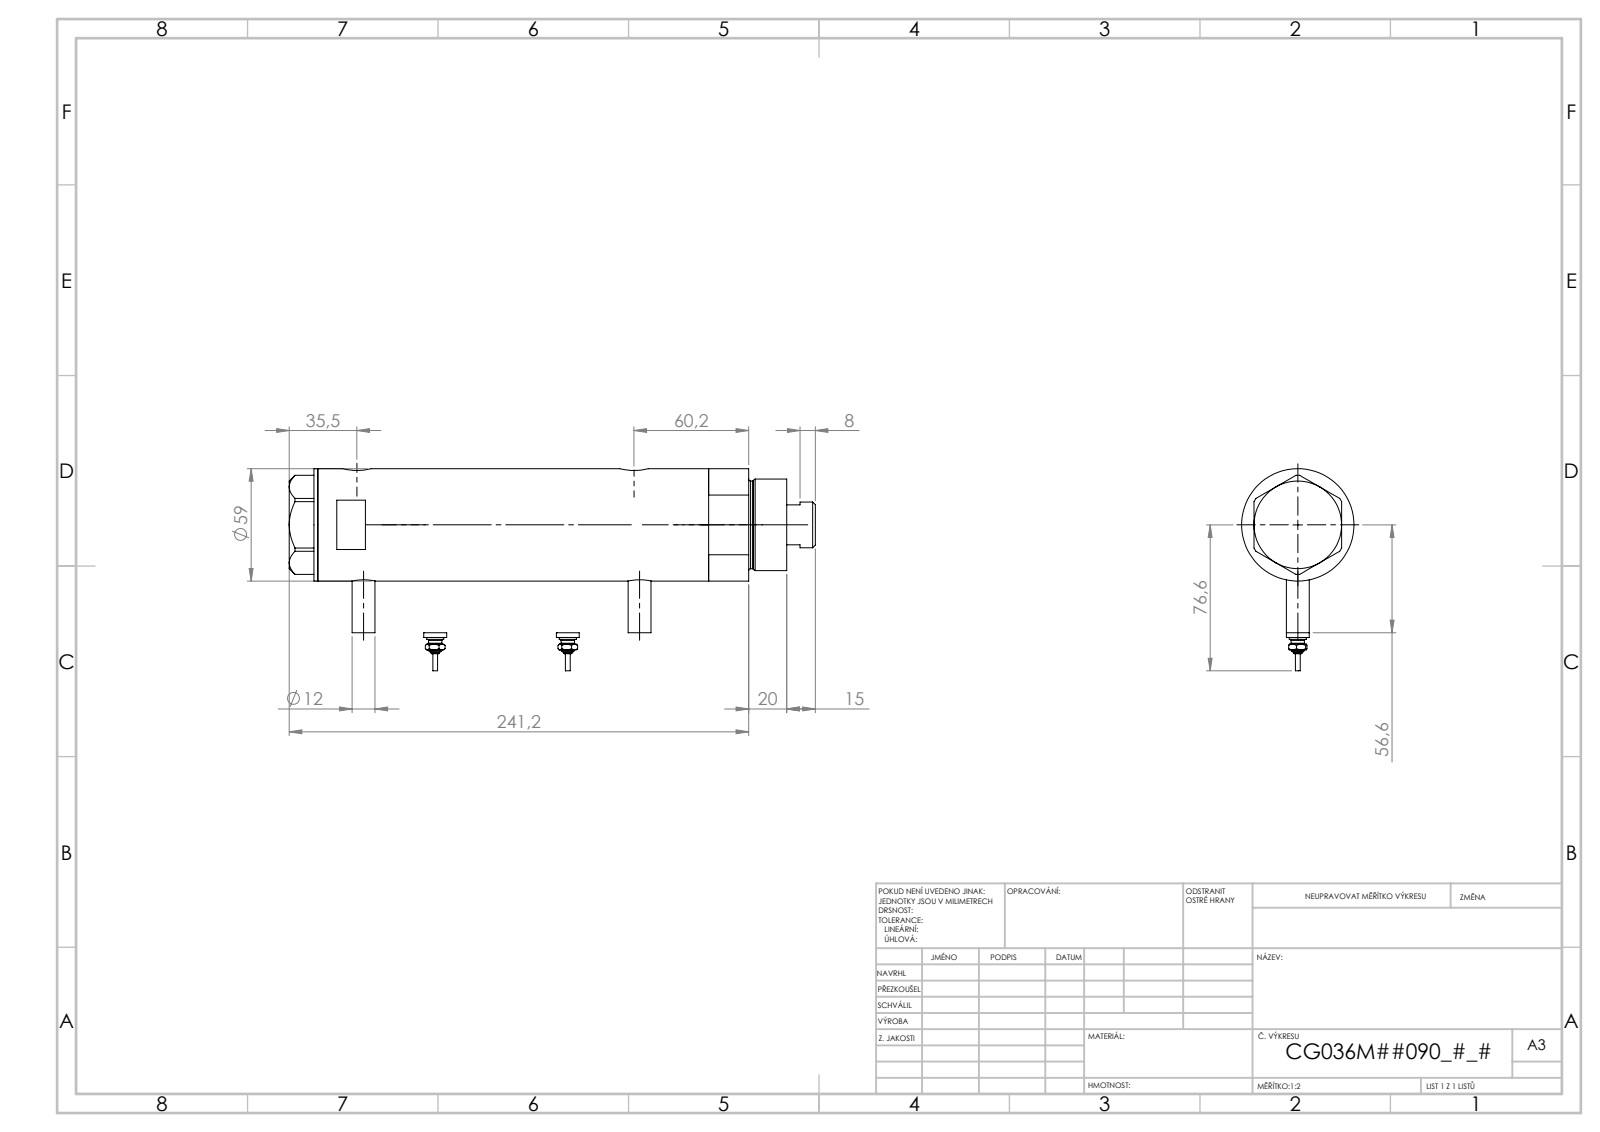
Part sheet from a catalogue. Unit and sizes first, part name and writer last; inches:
Units: inches
Overall size (bounding box): 9.977 × 3.594 × 2.323
Round holes (diameter × count): ⌀0.197 ×2, ⌀0.383 ×2, ⌀0.492 ×2, ⌀0.591 ×2, ⌀0.335 ×1, ⌀0.984 ×1, ⌀1.043 ×1, ⌀1.417 ×1, ⌀1.575 ×1, ⌀2.047 ×1
Round bosses / shafts (diameter × count): ⌀0.472 ×3, ⌀0.354 ×2, ⌀0.276 ×2, ⌀0.171 ×2, ⌀0.094 ×2, ⌀2.323 ×1, ⌀1.89 ×1, ⌀1.811 ×1
Main face-to-face distances: 5.801, 0.925, 4.876, 0.591, 1.516, 6.391, 9.387, 8.796, 7.871, 2.995
Hole centre spacings: 0.114, 0.138, 4.809, 4.923, 4.947, 5.061, 0.114, 0.115
Volume: 34.94 in³ · Surface area: 182.5 in²
Bodies: 6 solids, 232 faces (81 planar, 77 cylindrical, 74 other)
Part name (STEP PRODUCT): V270CG_BACK; V270CG_SWITCH; V270CG_MIDDLE; V270CG_VC (+1 more)
STEP written by: SolidWorks 2019 (CONFIG_CONTROL_DESIGN)
